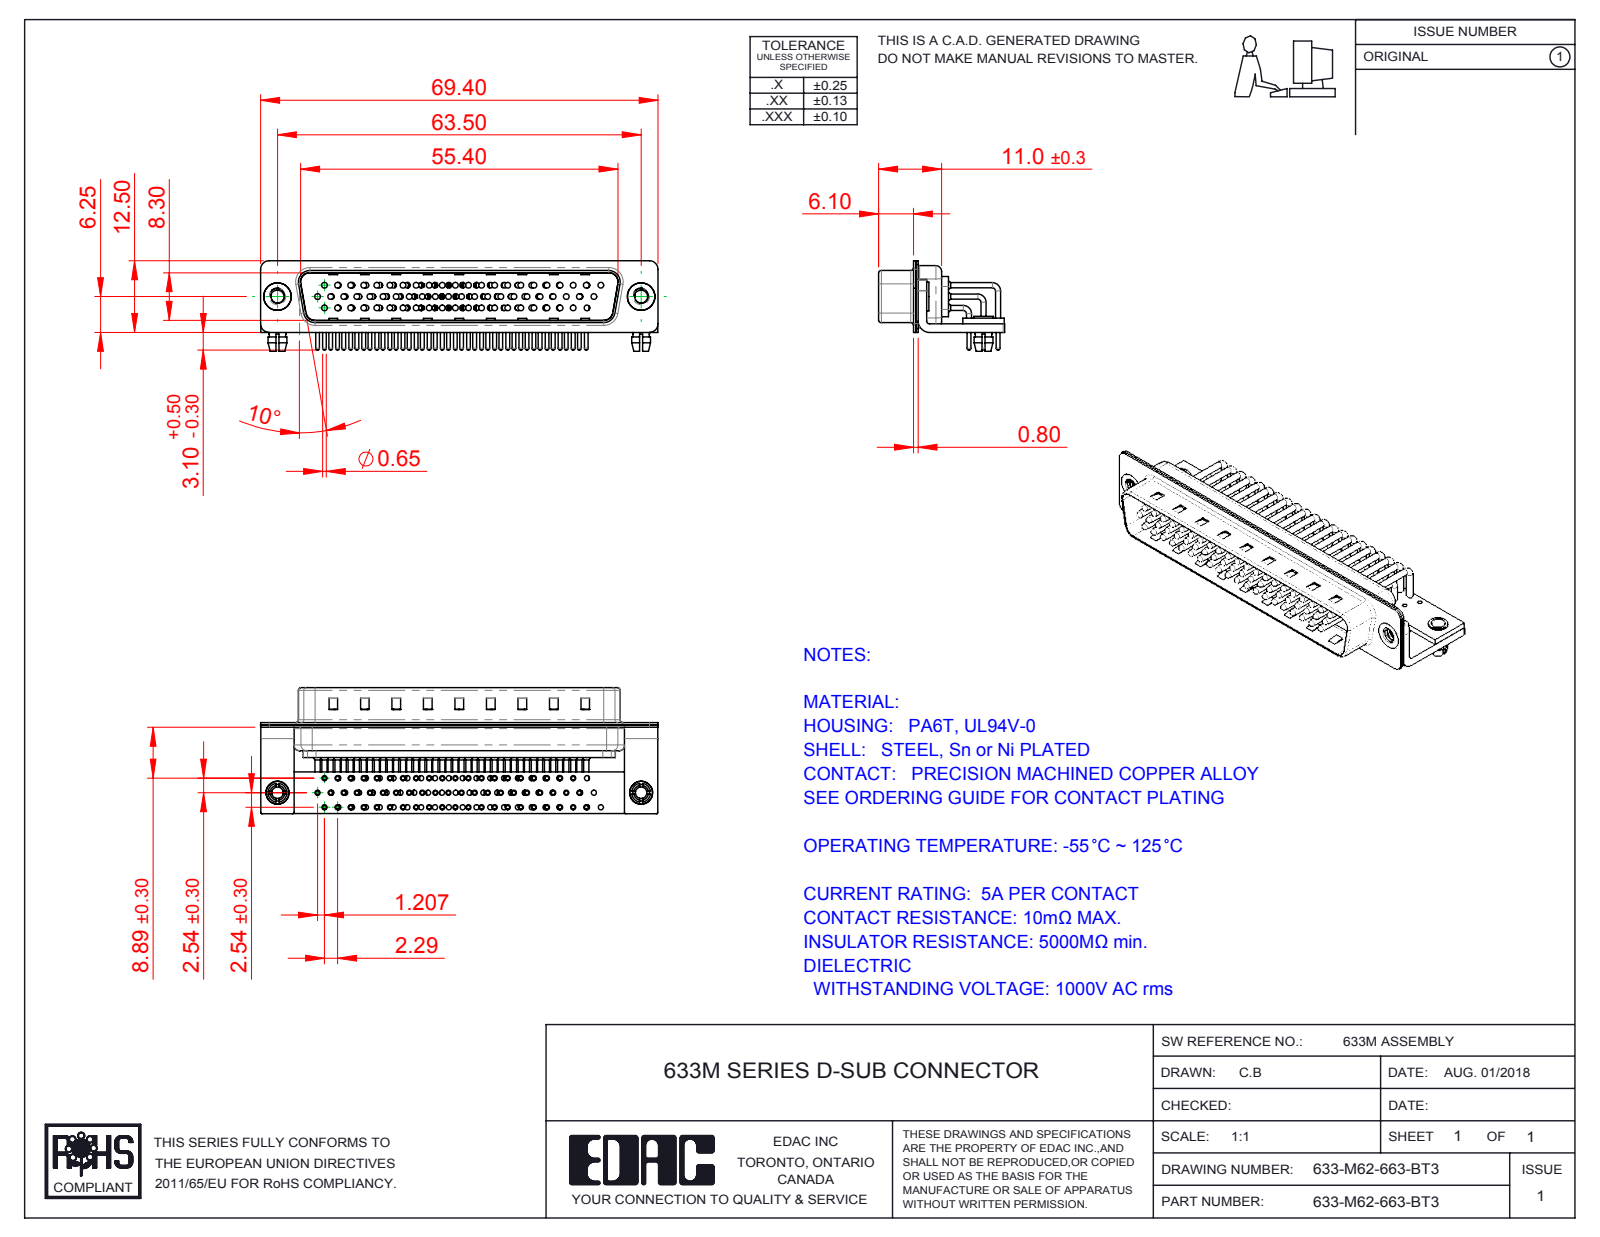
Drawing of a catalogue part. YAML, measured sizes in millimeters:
part_name: "633M Housing_62 Contacts; 633M Contact Row 3; 633M 4-40 Threaded Rivet_Stabilizer; 633M Stabilizer Board_62 Contacts (+7 more)"
step_written_by: "SolidWorks 2016 (CONFIG_CONTROL_DESIGN)"
units: millimeters
bodies: {solids: 72, faces: 7498, planar: 4245, cylindrical: 2551, other: 702}
overall_size: [69.4, 22, 15.8]
volume: 5119
surface_area: 15736
round_holes:
  - {diameter: 2, count: 64}
  - {diameter: 0.9, count: 62}
  - {diameter: 1, count: 62}
  - {diameter: 1.7, count: 62}
  - {diameter: 2.26, count: 2}
  - {diameter: 2.5, count: 2}
  - {diameter: 3.2, count: 2}
  - {diameter: 4, count: 2}
  - {diameter: 4.8, count: 2}
round_bosses_or_shafts:
  - {diameter: 0.9, count: 118}
  - {diameter: 1.5, count: 62}
  - {diameter: 0.65, count: 62}
  - {diameter: 1, count: 56}
  - {diameter: 5, count: 2}
  - {diameter: 4.9, count: 2}
  - {diameter: 4, count: 2}
  - {diameter: 3.4, count: 2}
partial_cylinders:
  - {radius: 1.01, count: 62}
  - {radius: 0.25, count: 16}
  - {radius: 1.5, count: 16}
  - {radius: 2, count: 13}
  - {radius: 0.5, count: 9}
  - {radius: 1.6, count: 8}
  - {radius: 0.6, count: 4}
  - {radius: 0.65, count: 4}
face_to_face_distances: [0.4, 0.85, 1.25, 1.5, 9.55, 1, 1.9, 10.4, 0.8, 8.3]
hole_center_spacings: [7.24, 2.41, 9.65, 4.83, 14.48, 16.89, 2.81, 2.32]
